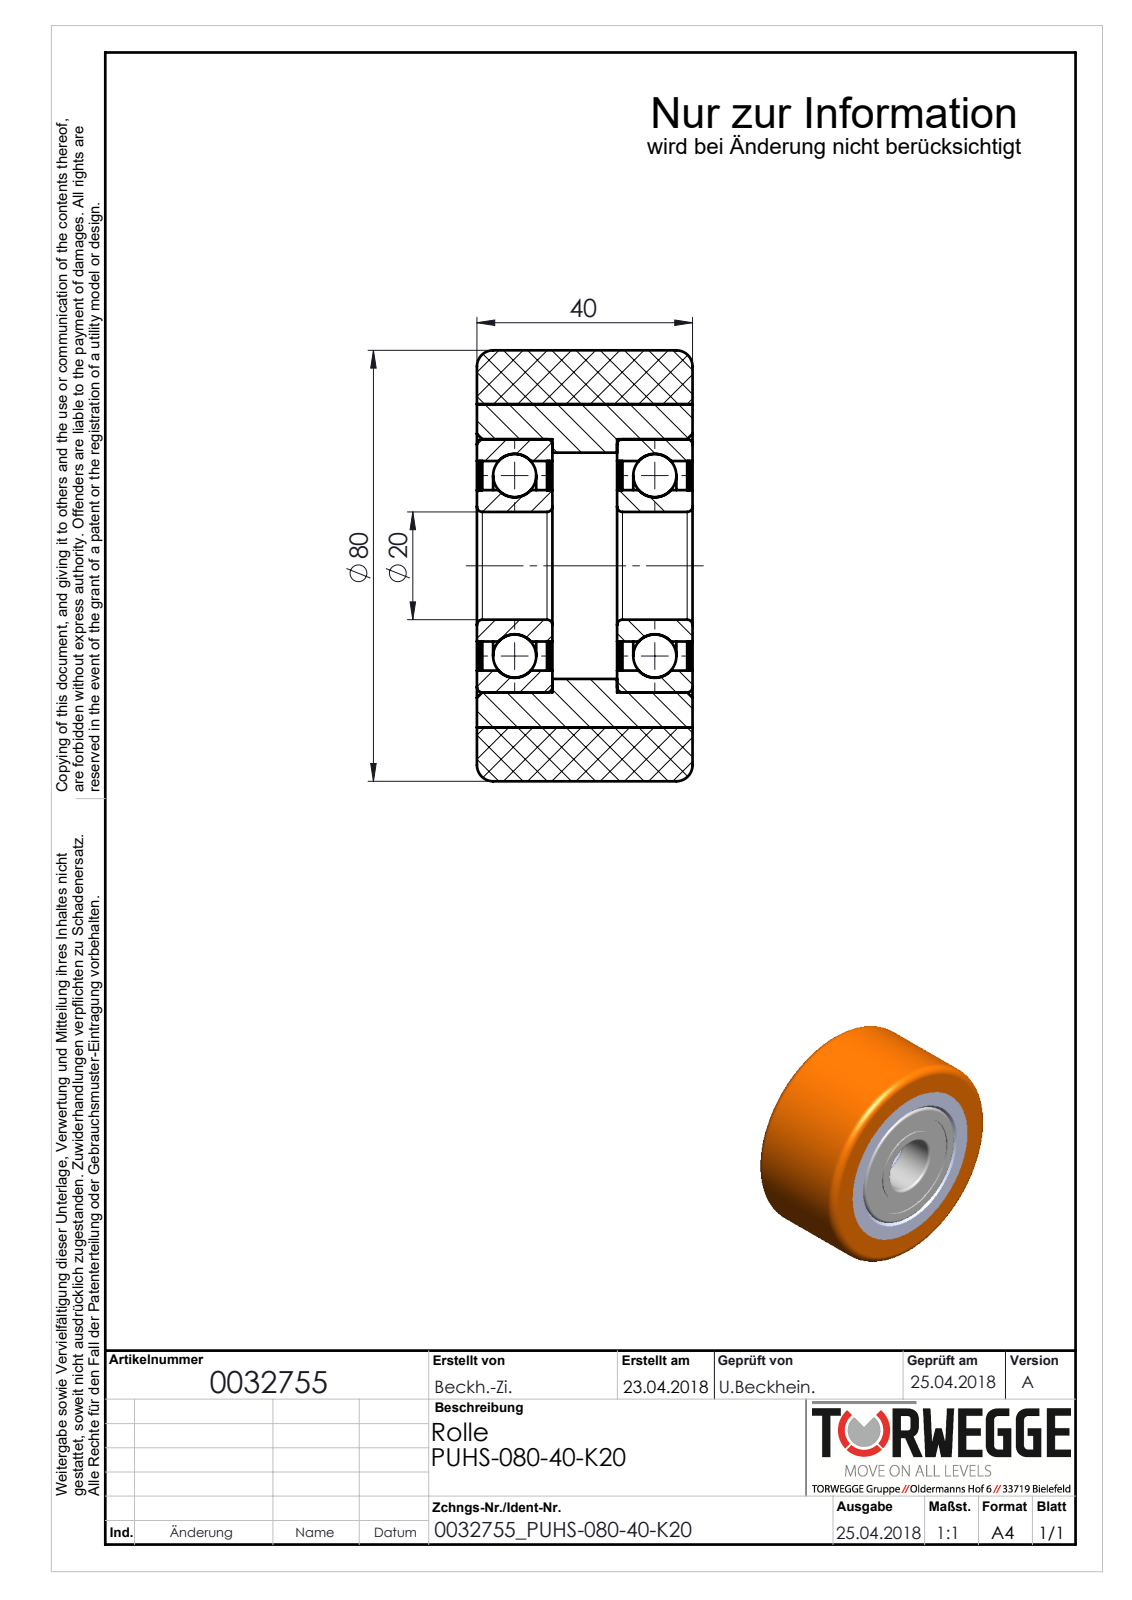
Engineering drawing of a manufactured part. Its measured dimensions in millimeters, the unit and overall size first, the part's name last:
Units: millimetres
Overall size (bounding box): 80 × 80 × 40
Round holes (diameter × count): ⌀20 ×1, ⌀28.1 ×1, ⌀38.9 ×1, ⌀42 ×1, ⌀47 ×1, ⌀60 ×1
Round bosses / shafts (diameter × count): ⌀80 ×1
Main face-to-face distances: 13, 0.5, 26, 13.5, 12.5, 40, 14, 1, 26.5, 25.5
Volume: 167 783 mm³ · Surface area: 62 727 mm²
Bodies: 12 solids, 66 faces (22 planar, 26 cylindrical, 18 other)
Part name (STEP PRODUCT): 0032755_PUHS-080-40-K20
STEP written by: SolidWorks 2018 (AUTOMOTIVE_DESIGN)
